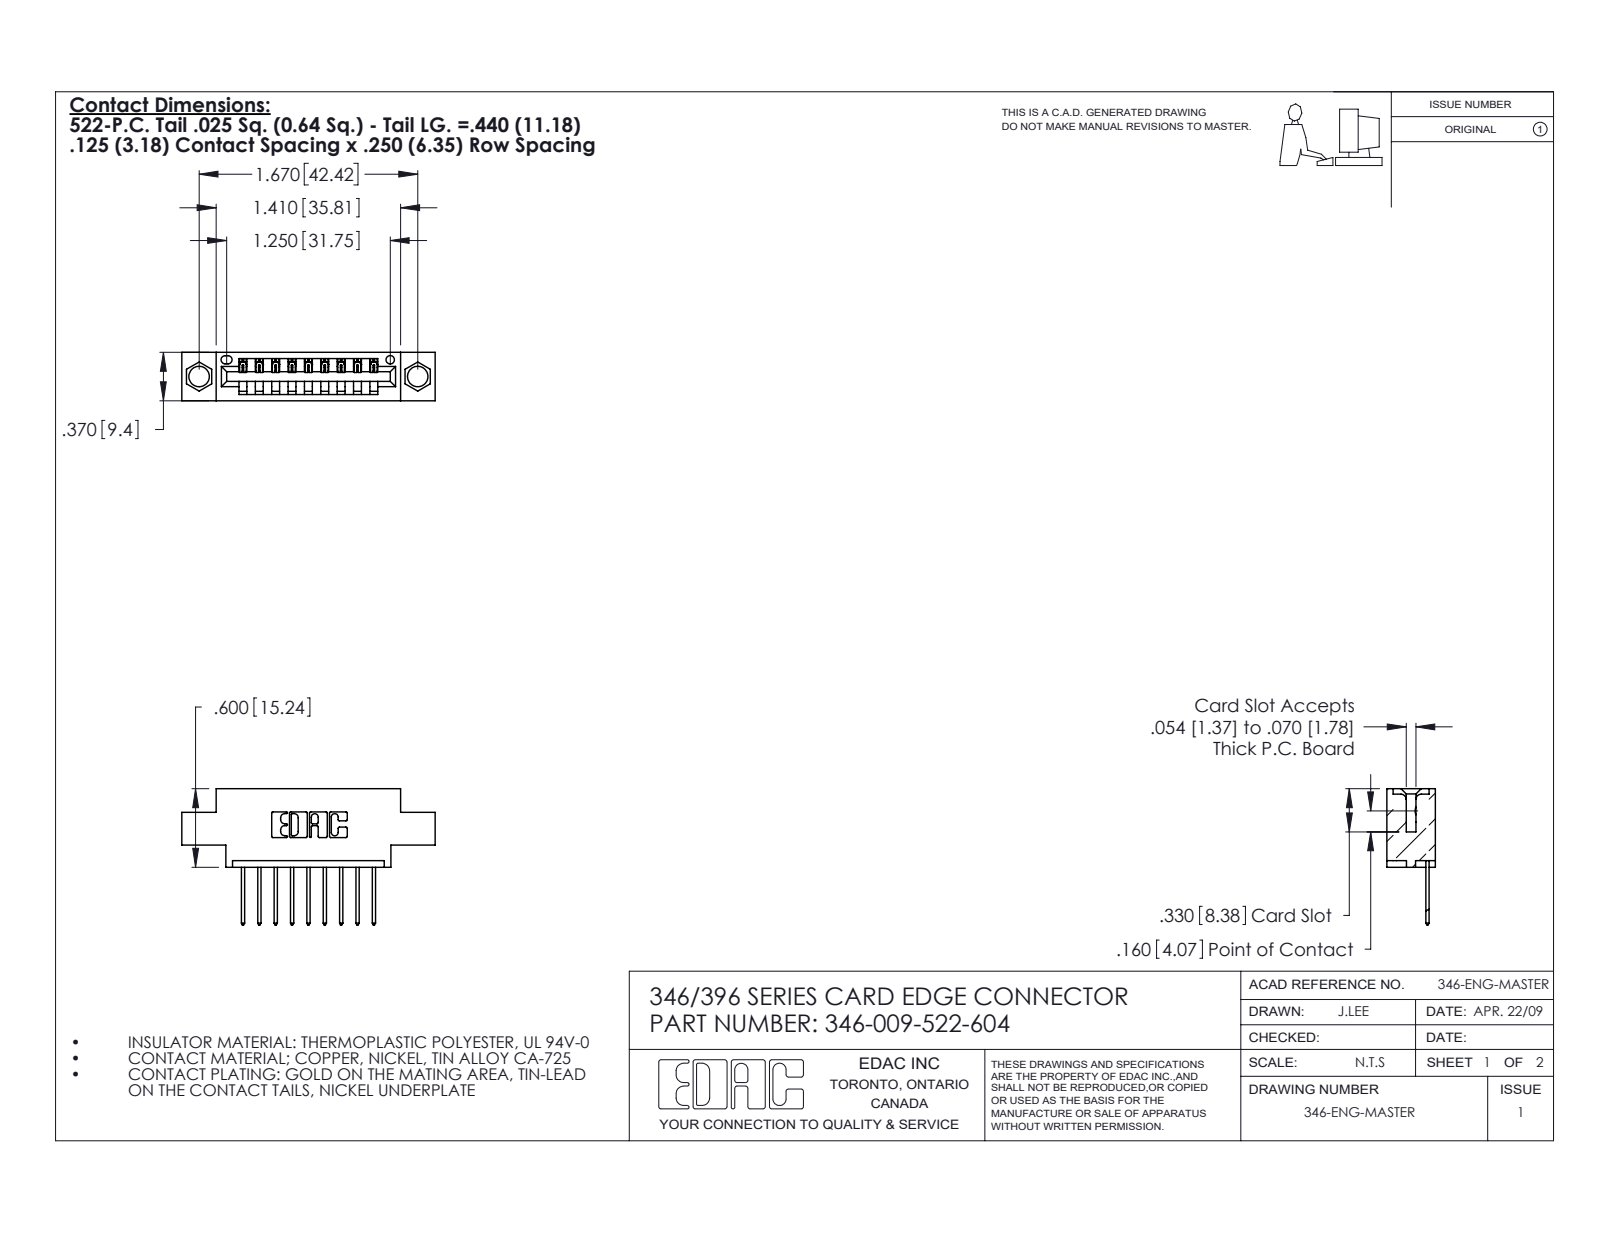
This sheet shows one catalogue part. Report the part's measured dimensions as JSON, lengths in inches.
{"part_name": "345-292-001_345-293-122; 346 Part_0.170 Offset - 0.156 Dia-TH; 346-009-522-604", "step_written_by": "SolidWorks 2020 (CONFIG_CONTROL_DESIGN)", "units": "inches", "bodies": {"solids": 10, "faces": 662, "planar": 454, "cylindrical": 208, "other": 0}, "overall_size": [1.935, 1.04, 0.37], "volume_in3": 0.257, "surface_area_in2": 7.667, "round_holes": [[0.156, 2], [0.064, 1]], "partial_cylinders_radius": [[0.01, 22], [0.006, 18], [0.01, 18], [0.007, 6], [0.031, 6], [0.026, 3], [0.031, 2], [0.04, 2]], "face_to_face_distances": [0.25, 0.37, 0.048, 0.322, 0.072, 0.298, 0.025, 0.222, 0.148, 0.1], "hole_center_spacings": [0.246, 1.465, 1.67]}
